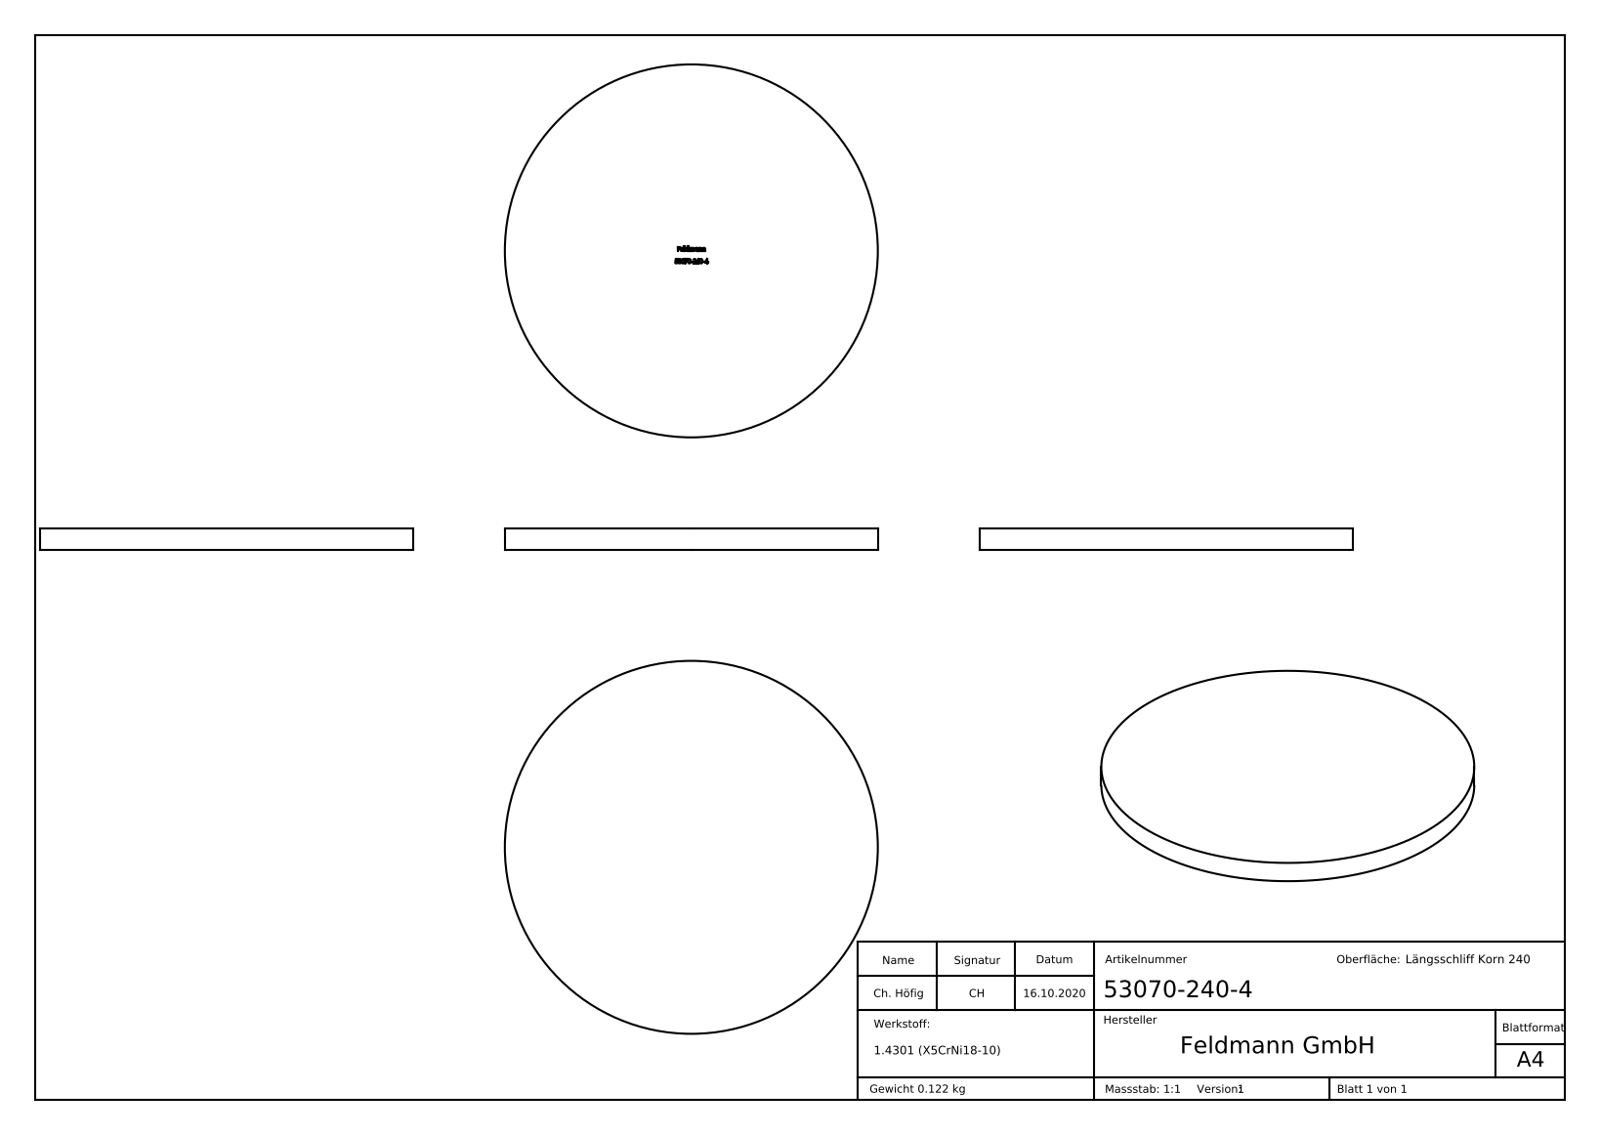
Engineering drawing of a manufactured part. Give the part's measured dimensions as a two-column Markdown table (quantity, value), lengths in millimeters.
| quantity | value |
| --- | --- |
| part name | 53070-240-4 |
| STEP written by | SolidWorks 2018 (CONFIG_CONTROL_DESIGN) |
| units | millimeters |
| bodies | 1 solid, 243 faces (138 planar, 2 cylindrical, 103 other) |
| overall size | 70 × 70 × 4 |
| volume | 15 394 mm³ |
| surface area | 8 583 mm² |
| round bosses / shafts (diameter × count) | 70 × 1 |
| main face-to-face distances | 4, 3.9, 0.83, 0.76, 1.78, 2.61, 0.99, 2.45, 0.53, 0.79 |
